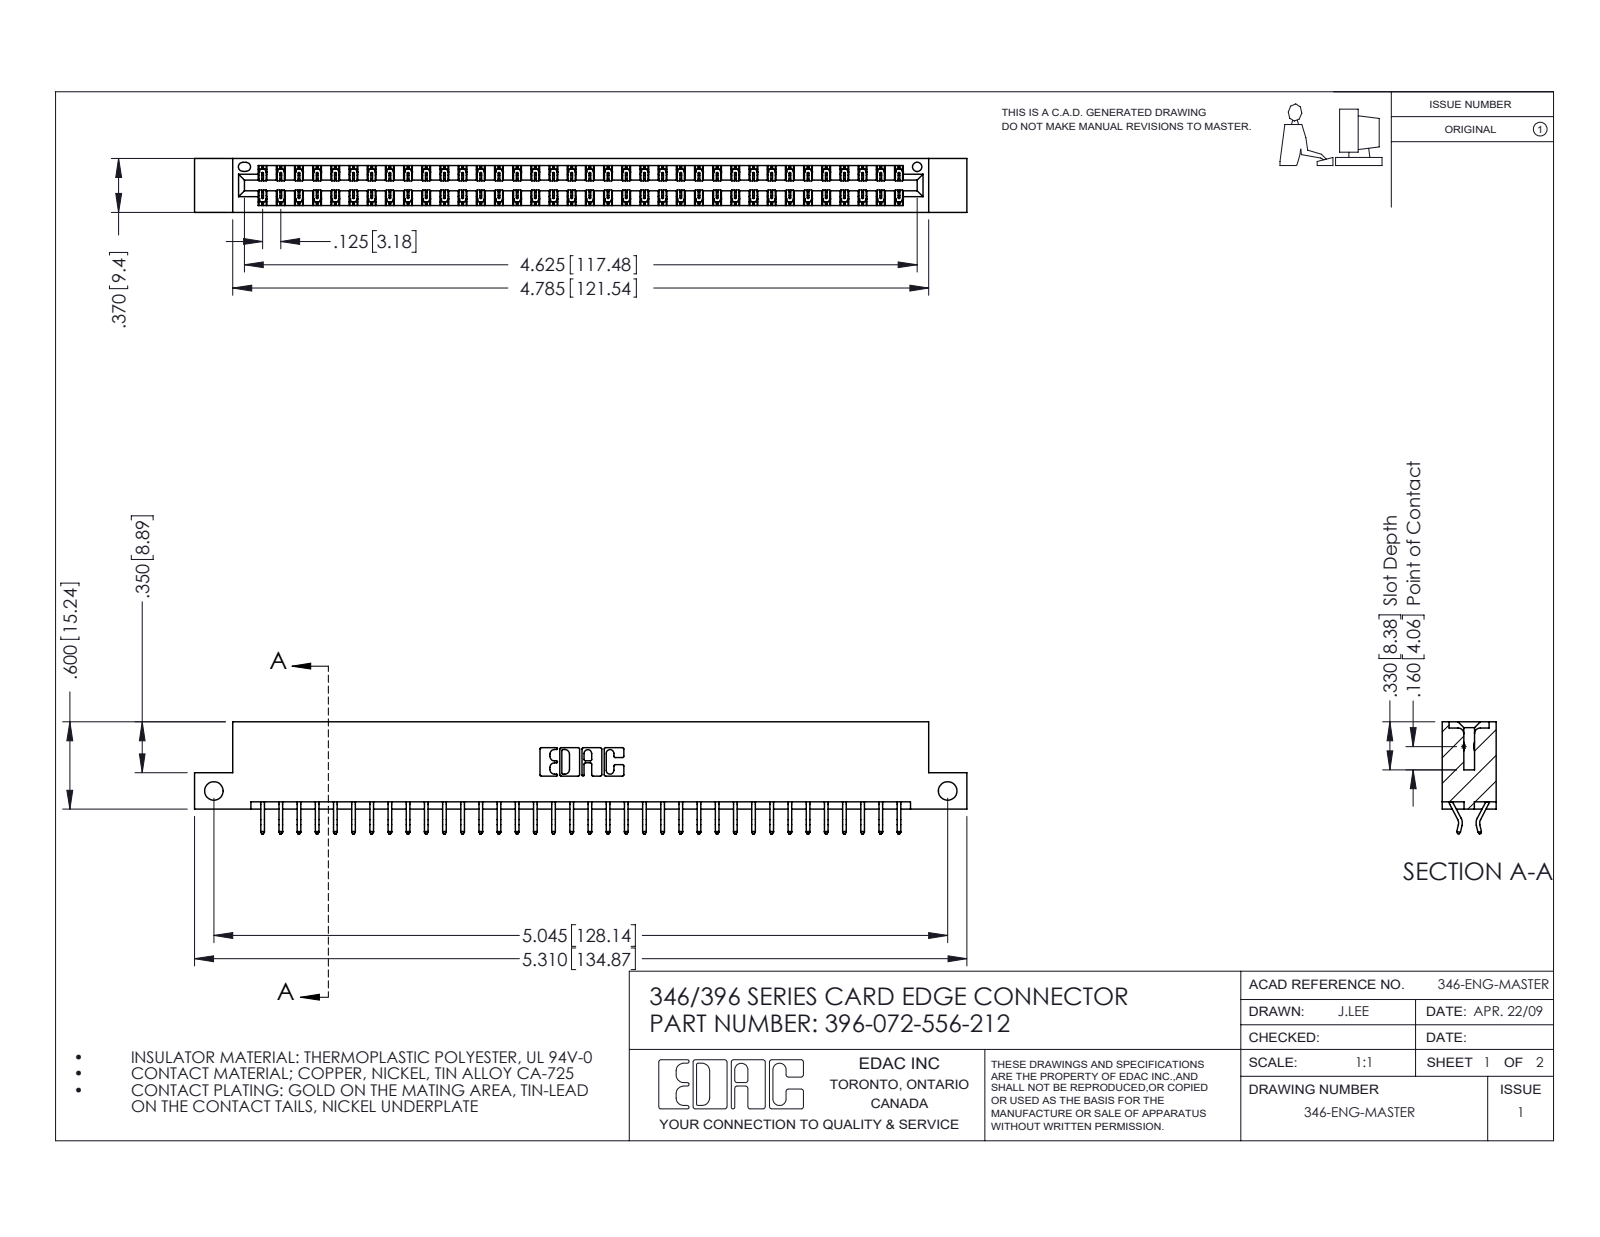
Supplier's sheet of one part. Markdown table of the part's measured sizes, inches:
| quantity | value |
| --- | --- |
| part name | 396-072-556-212; 345-292-001_556 Tail; 346 Part_Flush Mounting Lugs - Side Mount |
| STEP written by | SolidWorks 2016 (CONFIG_CONTROL_DESIGN) |
| units | inches |
| bodies | 73 solids, 4298 faces (2884 planar, 1414 cylindrical, 0 other) |
| overall size | 5.31 × 0.77 × 0.37 |
| volume | 0.794 in³ |
| surface area | 27.27 in² |
| round holes (diameter × count) | 0.128 × 2, 0.064 × 1 |
| partial cylindrical surfaces (radius × count) | 0.006 × 108, 0.01 × 22, 0.007 × 6, 0.031 × 6, 0.026 × 3, 0.01 × 2, 0.014 × 2, 0.022 × 2 |
| main face-to-face distances | 0.048, 0.322, 0.37, 0.25, 0.025, 0.072, 0.298, 0.275, 0.148, 0.222 |
| hole center spacings | 5.045 |
